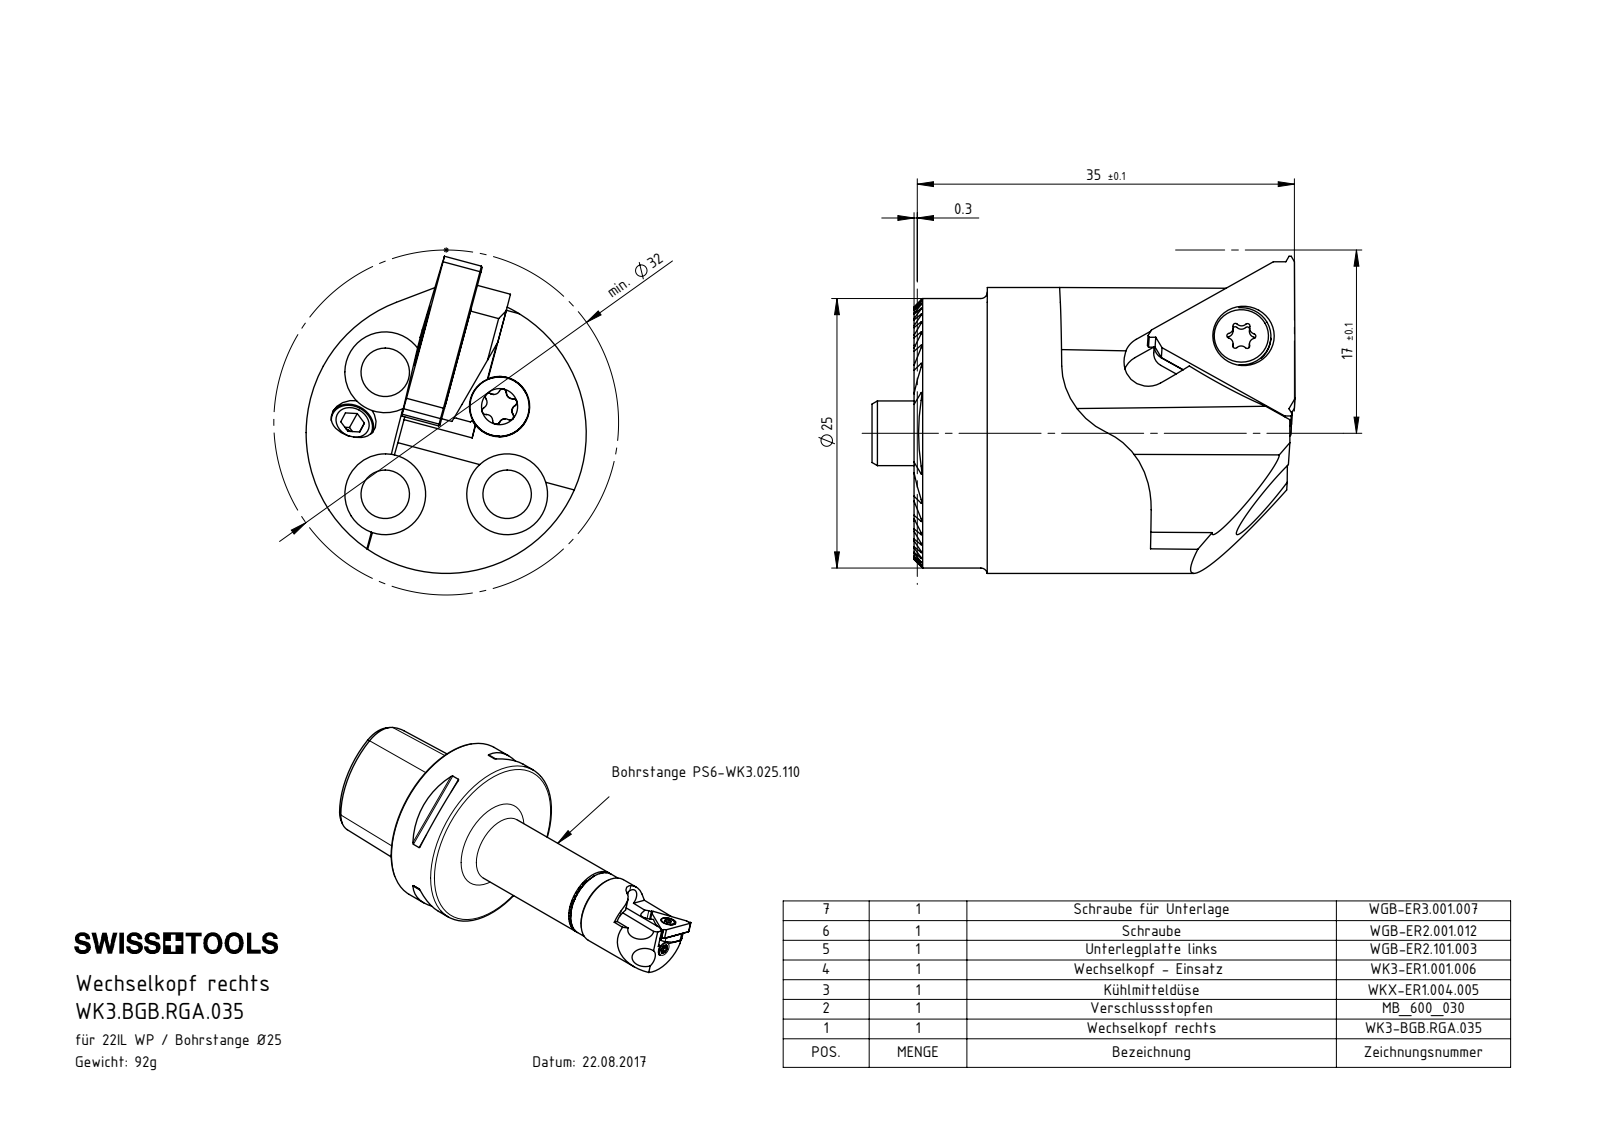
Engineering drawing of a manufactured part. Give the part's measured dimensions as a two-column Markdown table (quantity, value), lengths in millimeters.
| quantity | value |
| --- | --- |
| part name | WK3.BGB.RGA.035; WK3-BGB.RGA.035_B; WGB-ER3.001.007_A; KVT_MB_600_030 (+5 more) |
| STEP written by | SolidWorks 2017 (AUTOMOTIVE_DESIGN) |
| units | millimeters |
| bodies | 9 solids, 351 faces (198 planar, 98 cylindrical, 55 other) |
| overall size | 39.27 × 29.42 × 26 |
| volume | 11 405 mm³ |
| surface area | 7 192 mm² |
| round holes (diameter × count) | 4.5 × 3, 7.5 × 3, 2.58 × 2, 4.2 × 2, 1.7 × 1, 2.38 × 1, 2.5 × 1, 3 × 1, 3.3 × 1, 4 × 1, 4.02 × 1, 6 × 1 |
| round bosses / shafts (diameter × count) | 5.5 × 2, 3 × 2, 26 × 1, 25 × 1, 4 × 1, 3.18 × 1, 2.78 × 1 |
| partial cylindrical surfaces (radius × count) | 0.12 × 20, 0.23 × 6, 0.34 × 6, 0.57 × 6, 0.57 × 6, 0.1 × 2, 0.25 × 2, 7 × 2 |
| main face-to-face distances | 4.33, 1.08, 3.25, 5.41, 8.66, 7.58, 2.16, 2.17, 3.35, 9.74 |
| hole center spacings | 8, 11.32, 16.01 |
